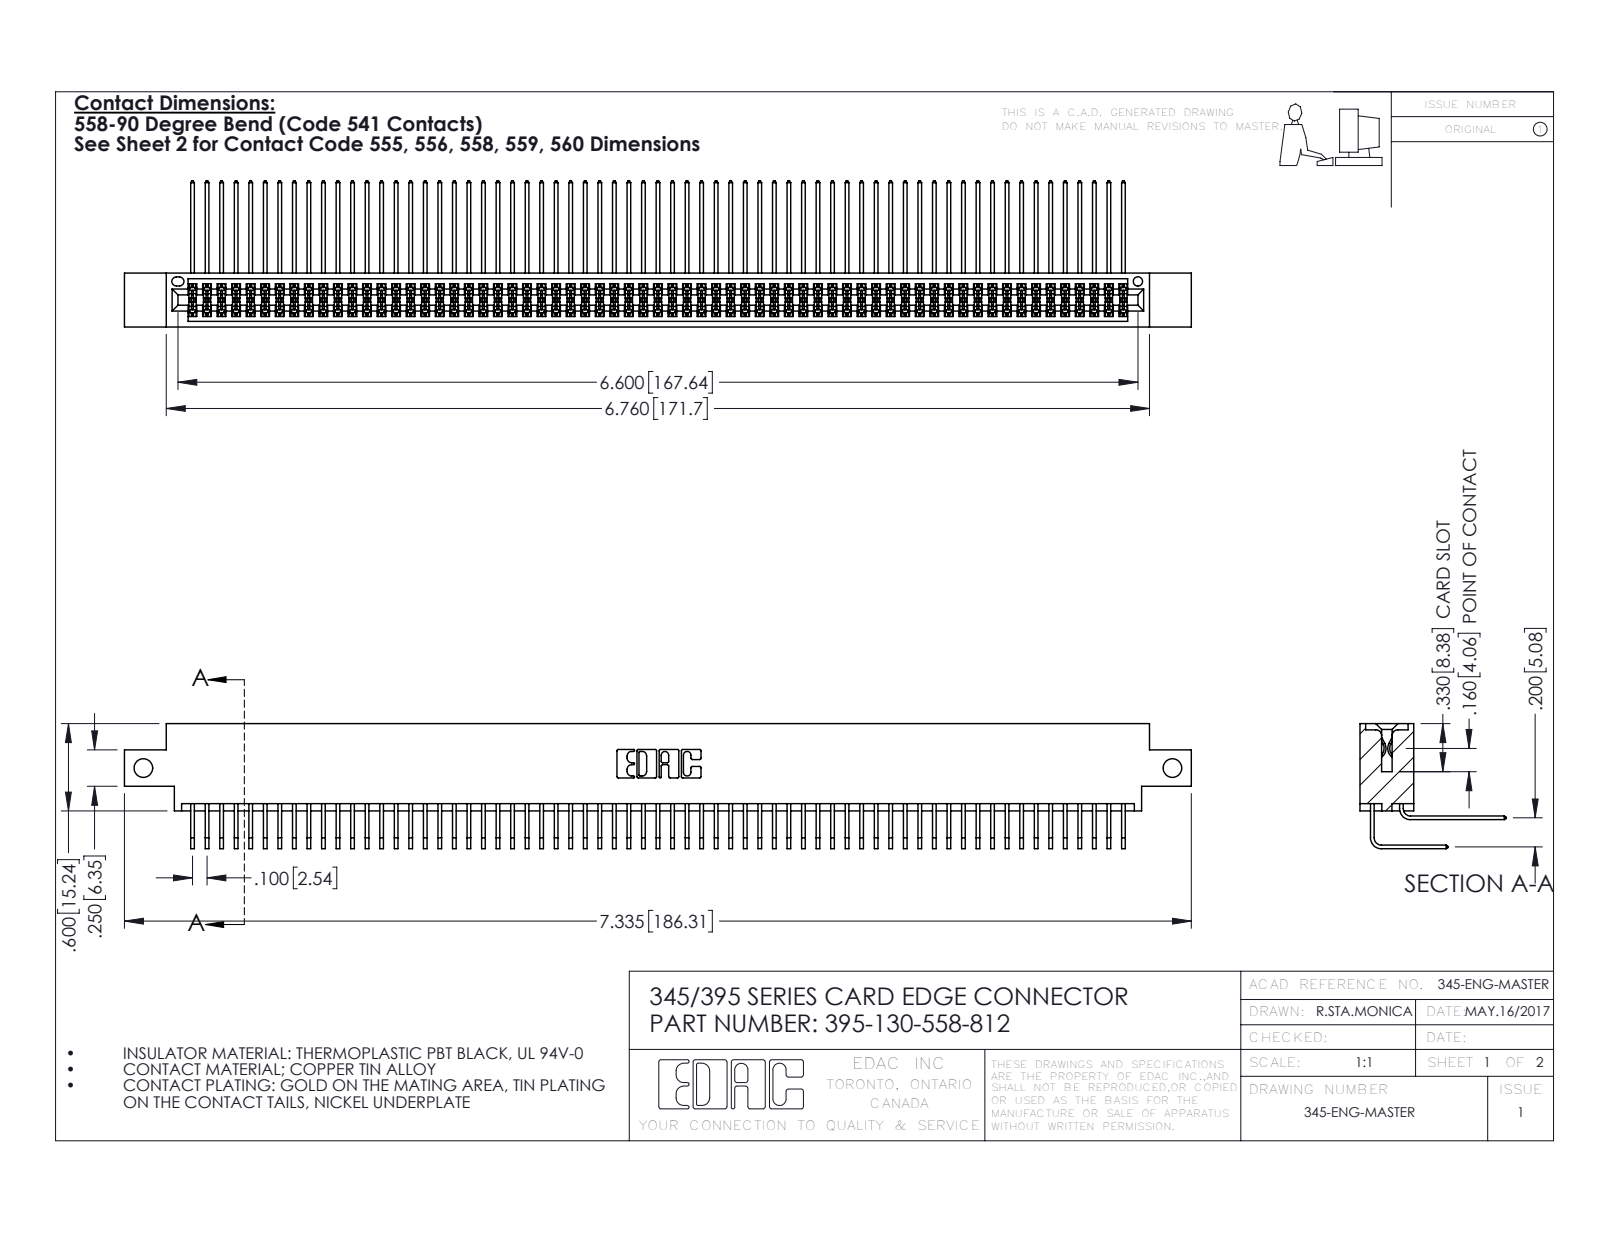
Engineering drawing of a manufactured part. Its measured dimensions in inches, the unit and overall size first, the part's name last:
Units: inches
Overall size (bounding box): 7.335 × 1.005 × 0.859
Round holes (diameter × count): ⌀0.128 ×2, ⌀0.064 ×1
Partial cylindrical surfaces — rounded edges, fillets, slot ends (radius × count): R0.006 ×196, R0.01 ×22, R0.007 ×6, R0.031 ×6, R0.026 ×3, R0.014 ×2, R0.019 ×2, R0.022 ×2
Main face-to-face distances: 0.072, 0.298, 0.2, 0.37, 0.098, 0.272, 0.025, 0.225, 0.175, 0.025
Hole centre spacings: 7.075
Volume: 1.151 in³ · Surface area: 49.38 in²
Bodies: 131 solids, 6890 faces (4634 planar, 2256 cylindrical, 0 other)
Part name (STEP PRODUCT): 395-130-558-812; 345 Part_0.170 Offset - Side Mount; 345-292-001_558 Tail - 2; 345-292-001_558 559 Tail - 1
STEP written by: SolidWorks 2016 (CONFIG_CONTROL_DESIGN)
